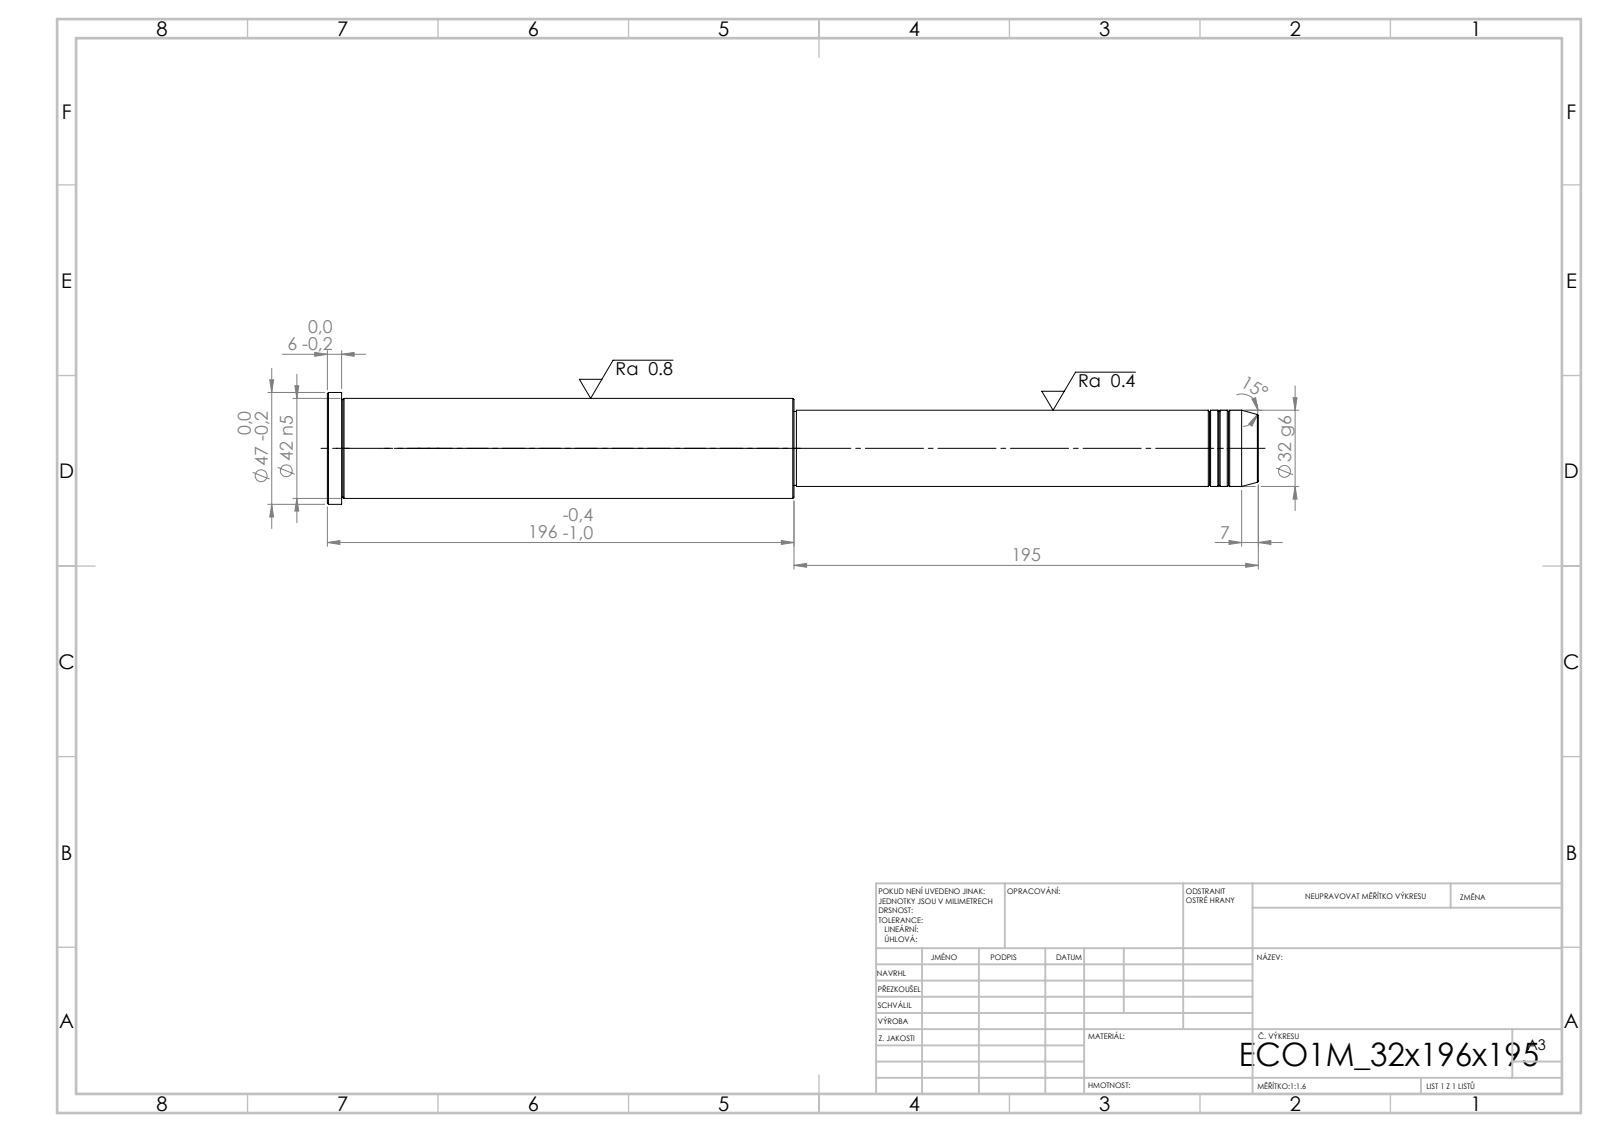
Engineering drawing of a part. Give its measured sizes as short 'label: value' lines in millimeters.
written by: SolidWorks 2019 (CONFIG_CONTROL_DESIGN)
unit: mm
bodies: 1 solid, 43 faces (5 planar, 14 cylindrical, 24 other)
size: 391 × 47 × 47
volume: 429 583 mm³; area: 49 072 mm²
bosses: 1× ⌀47, 1× ⌀42, 1× ⌀32, 1× ⌀31
face distances: 391, 195, 196, 385, 190, 6, 194, 1, 191, 197
